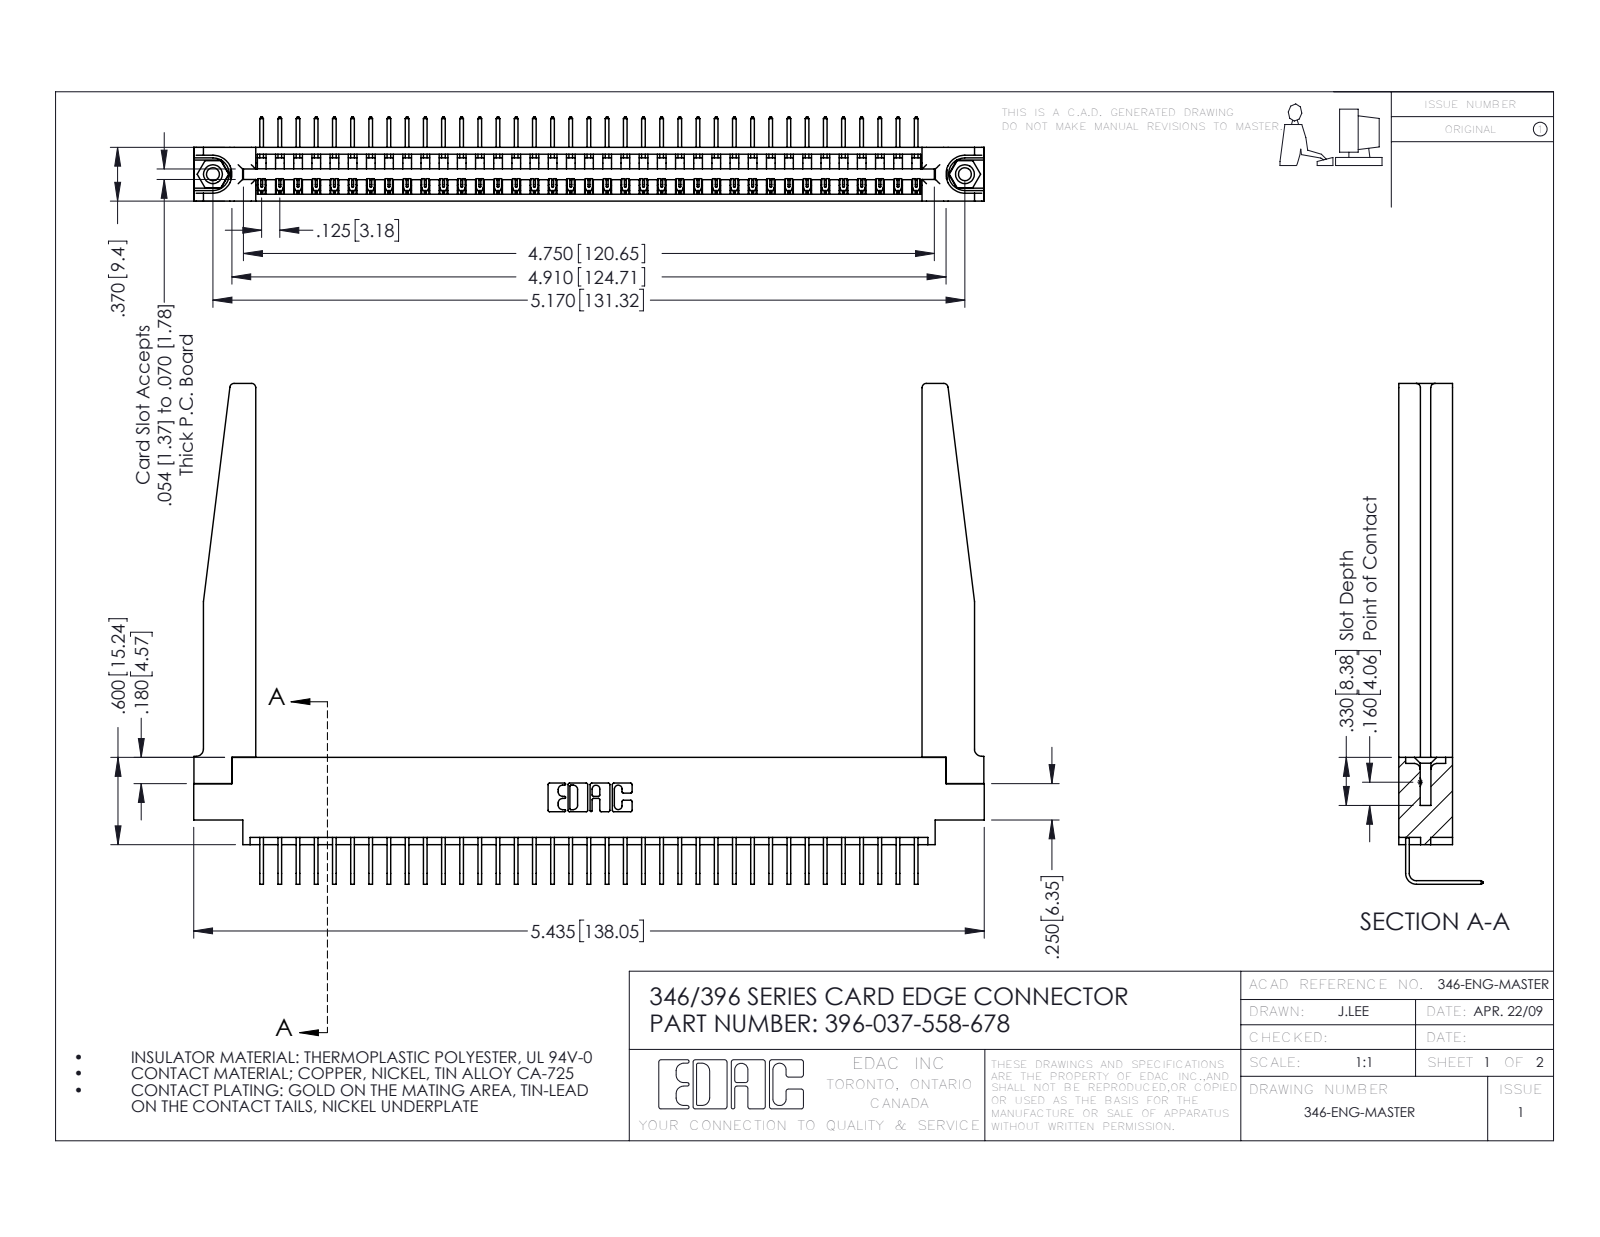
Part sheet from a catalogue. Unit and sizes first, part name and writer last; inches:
Units: inches
Overall size (bounding box): 5.435 × 3.443 × 0.58
Round holes (diameter × count): ⌀0.089 ×2, ⌀0.125 ×2, ⌀0.156 ×2, ⌀0.064 ×1
Round bosses / shafts (diameter × count): ⌀0.155 ×2
Partial cylindrical surfaces — rounded edges, fillets, slot ends (radius × count): R0.006 ×74, R0.01 ×22, R0.03 ×8, R0.007 ×6, R0.031 ×6, R0.026 ×3, R0.05 ×3, R0.031 ×2
Main face-to-face distances: 0.37, 0.322, 0.048, 0.072, 0.148, 0.15, 0.298, 0.025, 0.25, 0.222
Hole centre spacings: 0.246, 4.961, 5.17
Volume: 1.224 in³ · Surface area: 36.91 in²
Bodies: 42 solids, 2580 faces (1776 planar, 752 cylindrical, 52 other)
Part name (STEP PRODUCT): 346 Part_0.170 Offset - 0.156 Dia-TH; 345-250-001_345-250-001-102; 345-292-001_558 Tail - 2; 346-220-078_345-220-078 (+1 more)
STEP written by: SolidWorks 2016 (CONFIG_CONTROL_DESIGN)
